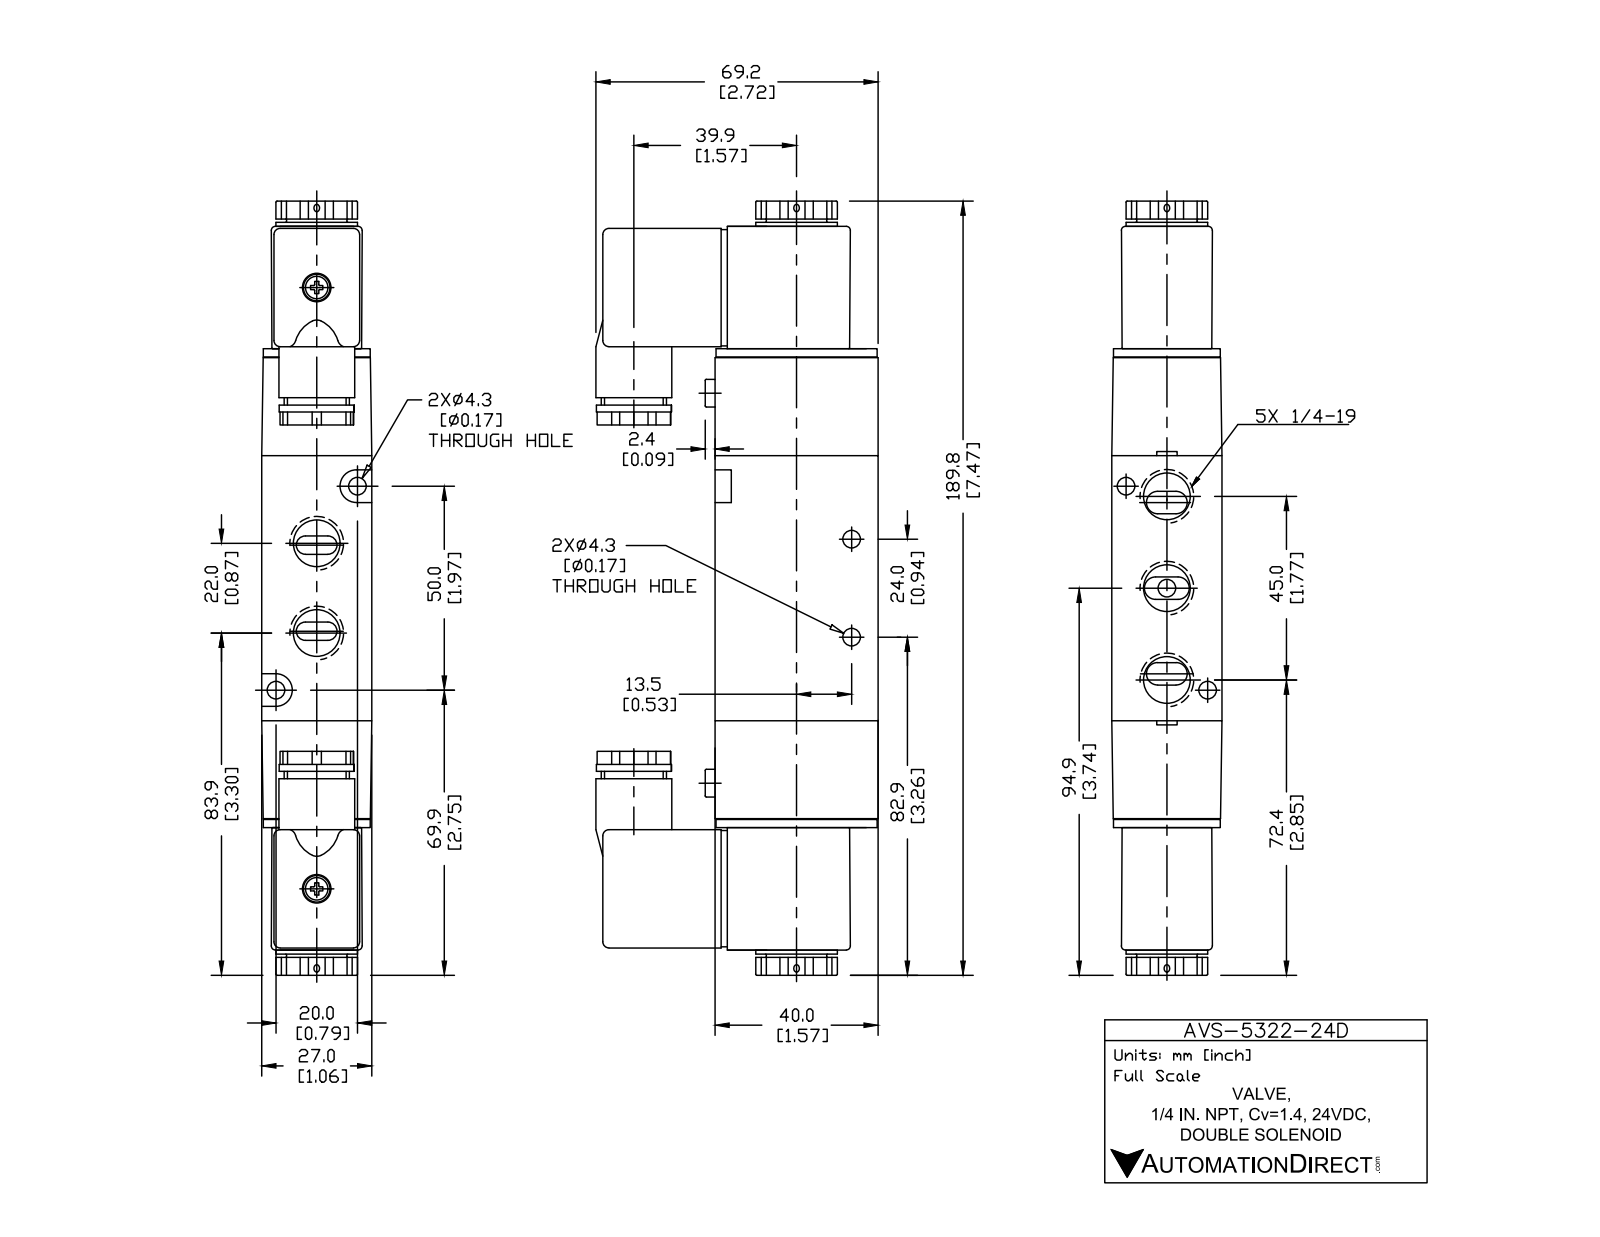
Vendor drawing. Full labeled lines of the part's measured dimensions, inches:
Part name (STEP PRODUCT): AVS-5322-24D
STEP written by: SolidWorks 2015 (CONFIG_CONTROL_DESIGN)
Units: inches
Bodies: 5 solids, 272 faces (127 planar, 111 cylindrical, 34 other)
Overall size (bounding box): 7.472 × 2.724 × 1.063
Volume: 12.46 in³ · Surface area: 66.66 in²
Round holes (diameter × count): ⌀0.438 ×5, ⌀0.169 ×4, ⌀0.366 ×1
Round bosses / shafts (diameter × count): ⌀0.264 ×2, ⌀0.787 ×1, ⌀0.732 ×1, ⌀0.724 ×1, ⌀0.63 ×1, ⌀0.583 ×1
Partial cylindrical surfaces — rounded edges, fillets, slot ends (radius × count): R0.059 ×18, R0.039 ×10, R0.061 ×10, R0.02 ×8, R0.118 ×2
Main face-to-face distances: 1.063, 0.118, 0.945, 1.575, 2.559, 0.908, 0.827, 1.161, 0.02, 5.803
Hole centre spacings: 0.406, 0.433, 0.453, 0.677, 0.886, 1.06, 1.319, 1.471
